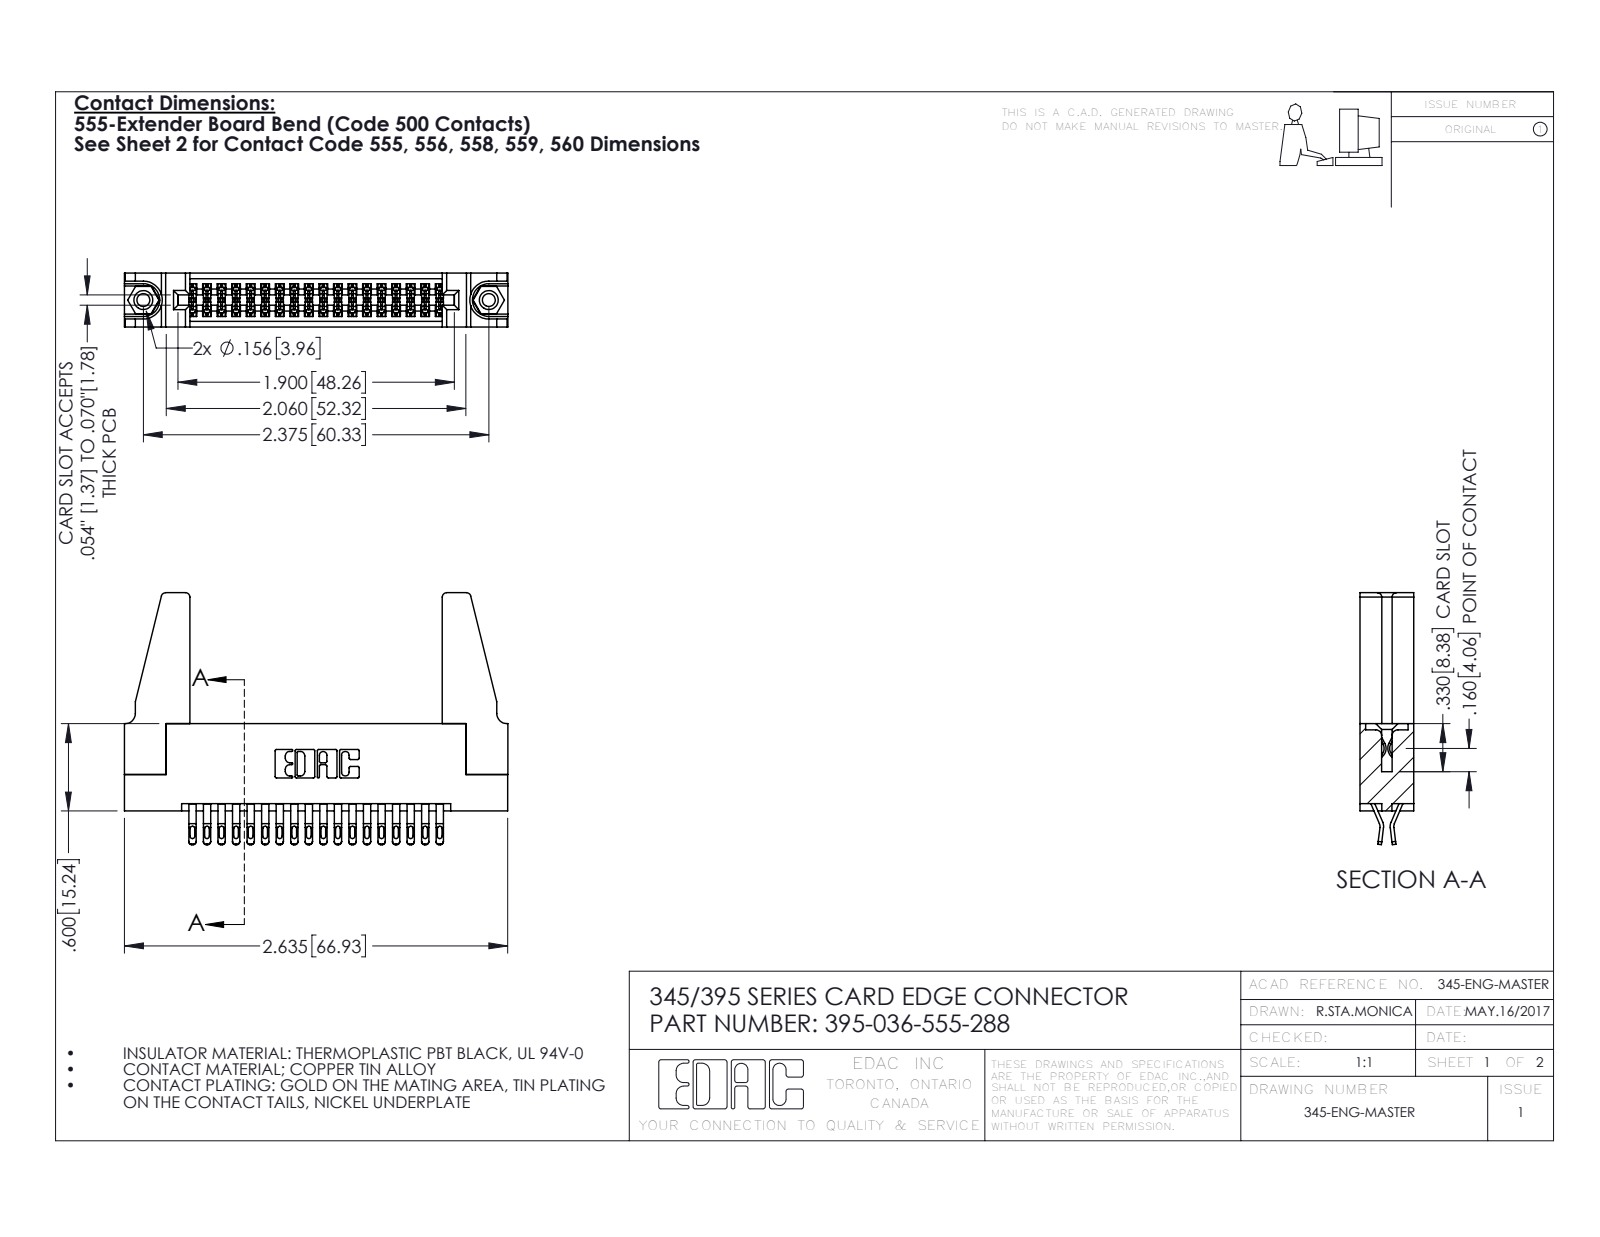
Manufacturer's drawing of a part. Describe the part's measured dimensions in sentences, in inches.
The part is named "395-036-555-288; 345-220-078_345-220-088; 345 Part_Flush Mounting Lugs - 0.156 Dia-TH; 345-250-001_345-250-001-102 (+1 more)". Its 3-D file was written by "SolidWorks 2016 (CONFIG_CONTROL_DESIGN)". It is 41 solids with 2266 faces: 1268 planar, 982 cylindrical and 16 other. Overall it measures 2.636 by 1.732 by 0.37 inches. Its volume is 0.588 cubic inches and its surface area 19.31 square inches. Round holes: 2 of diameter 0.089, 2 of diameter 0.125, 2 of diameter 0.156, 1 of diameter 0.064. Round bosses or shafts: 2 of diameter 0.155. Partial cylindrical surfaces (rounded edges, fillets, slot ends): 90 of radius 0.016, 72 of radius 0.02, 54 of radius 0.006, 22 of radius 0.01, 8 of radius 0.03, 6 of radius 0.007, 6 of radius 0.031, 3 of radius 0.026. The main face-to-face distances are 0.37, 0.072, 0.298, 0.2, 0.025, 0.098, 0.272, 0.225, 0.175, 0.15. The hole center spacings are 0.27, 2.141, 2.375.
